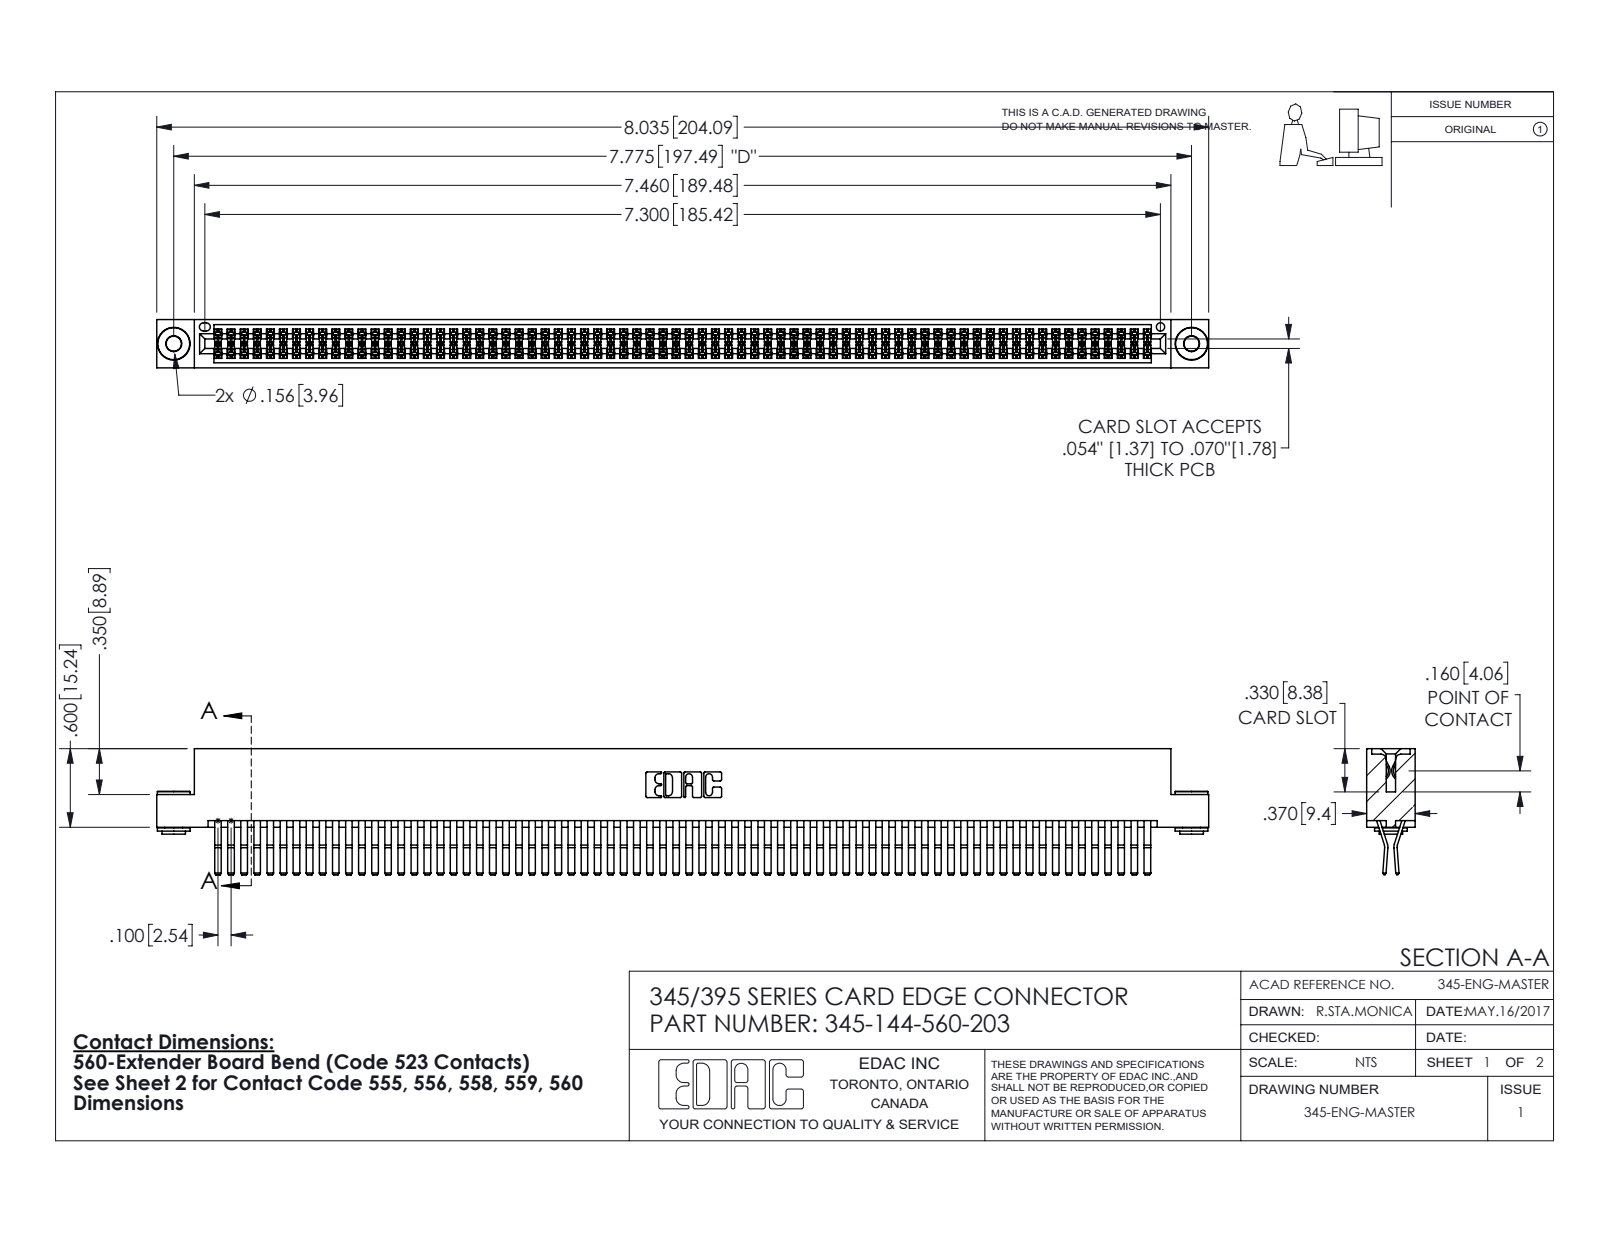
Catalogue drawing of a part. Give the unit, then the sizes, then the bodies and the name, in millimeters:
Units: millimetres
Overall size (bounding box): 204.1 × 24.4 × 9.4
Round holes (diameter × count): ⌀2.9 ×2, ⌀4 ×2, ⌀1.6 ×1
Round bosses / shafts (diameter × count): ⌀6.4 ×2, ⌀4.6 ×2, ⌀3.5 ×2
Partial cylindrical surfaces — rounded edges, fillets, slot ends (radius × count): R0.2 ×216, R0.3 ×22, R0.2 ×6, R0.8 ×6, R0.7 ×3, R0.3 ×2, R0.4 ×2, R0.5 ×2
Main face-to-face distances: 0.6, 1.8, 7.6, 5.1, 9.4, 2.5, 6.9, 5.7, 4.4, 3.8
Hole centre spacings: 6.9, 191.5, 197.5
Volume: 21 070 mm³ · Surface area: 34 350 mm²
Bodies: 147 solids, 7652 faces (4842 planar, 2802 cylindrical, 8 other)
Part name (STEP PRODUCT): 345-144-560-203; 345 Part_Flush Mounting Lugs - 0.156 Dia-TH; 345-250-002_345-250-002-102; 345-292-001_560 Tail
STEP written by: SolidWorks 2016 (CONFIG_CONTROL_DESIGN)
